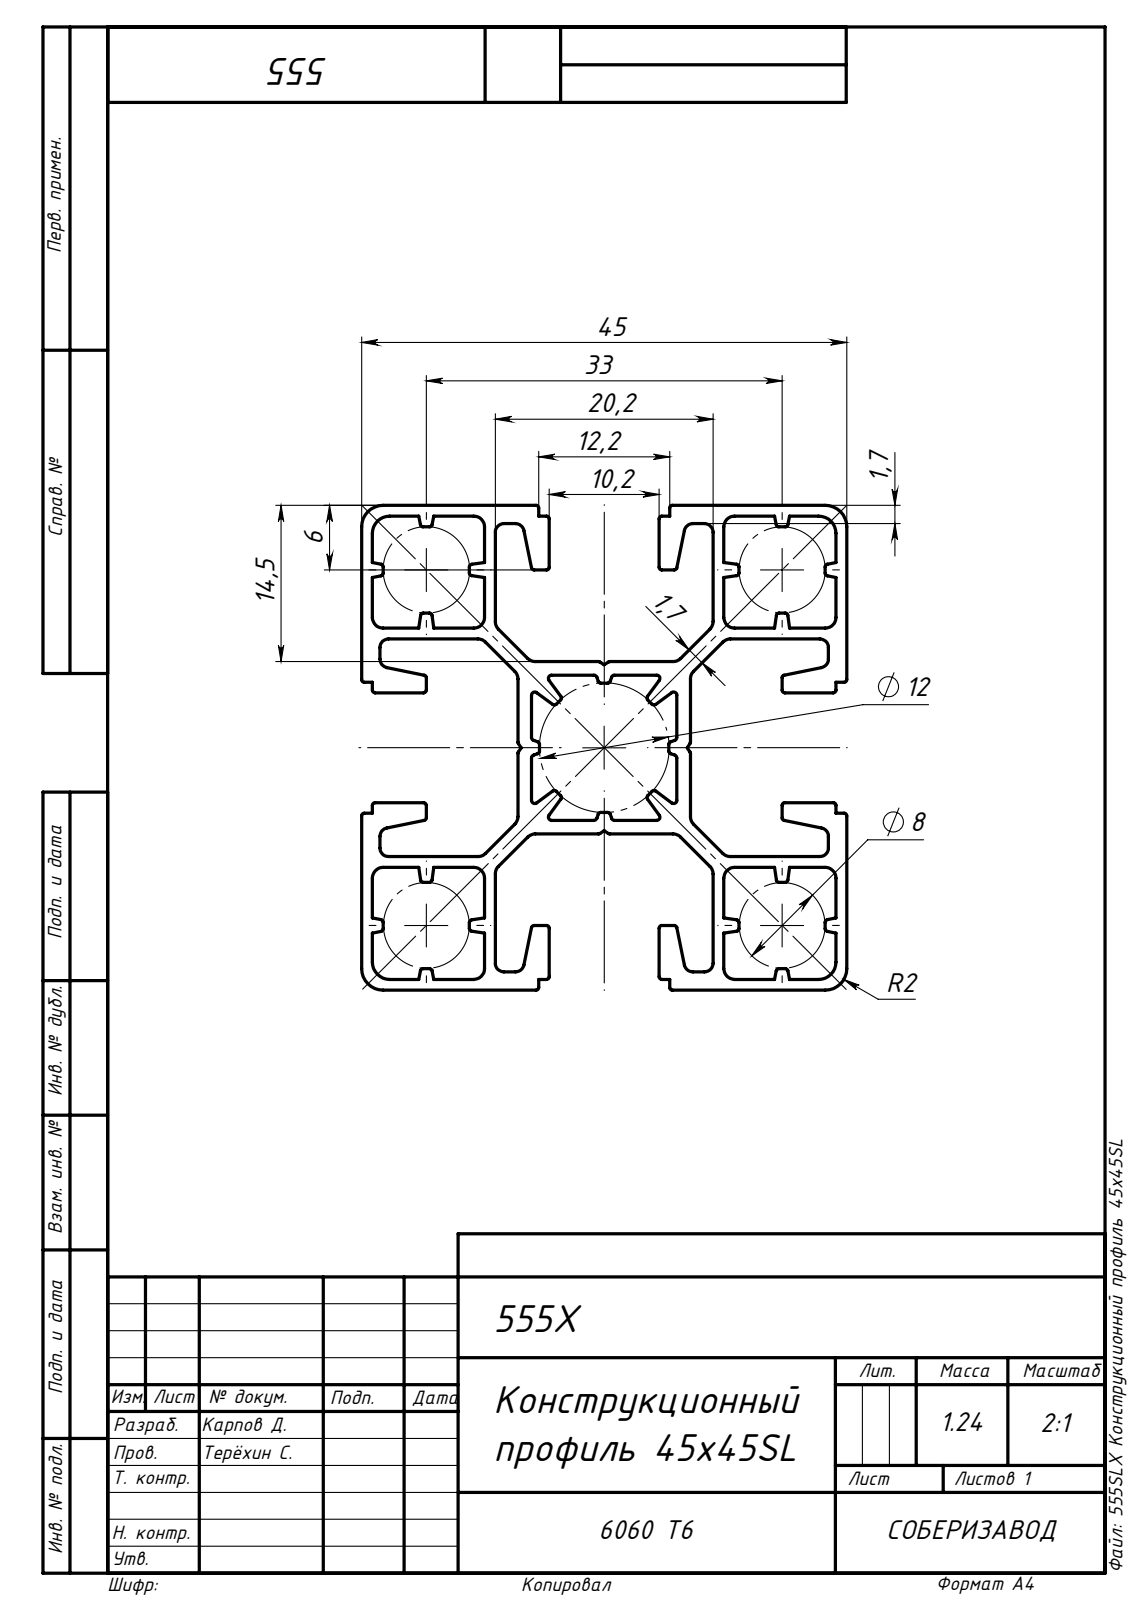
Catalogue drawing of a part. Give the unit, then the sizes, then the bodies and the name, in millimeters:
Units: millimetres
Overall size (bounding box): 1001 × 45 × 45
Partial cylindrical surfaces — rounded edges, fillets, slot ends (radius × count): R0.25 ×88, R1 ×28, R0.3 ×16, R0.8 ×16, R1.6 ×4, R2 ×4
Main face-to-face distances: 32.6, 11.4, 1, 12.4, 31.6, 10.4, 44, 45, 33.6, 21.2
Volume: 460 949 mm³ · Surface area: 670 055 mm²
Bodies: 1 solid, 366 faces (202 planar, 164 cylindrical, 0 other)
STEP written by: SolidWorks 2019 (AUTOMOTIVE_DESIGN)
